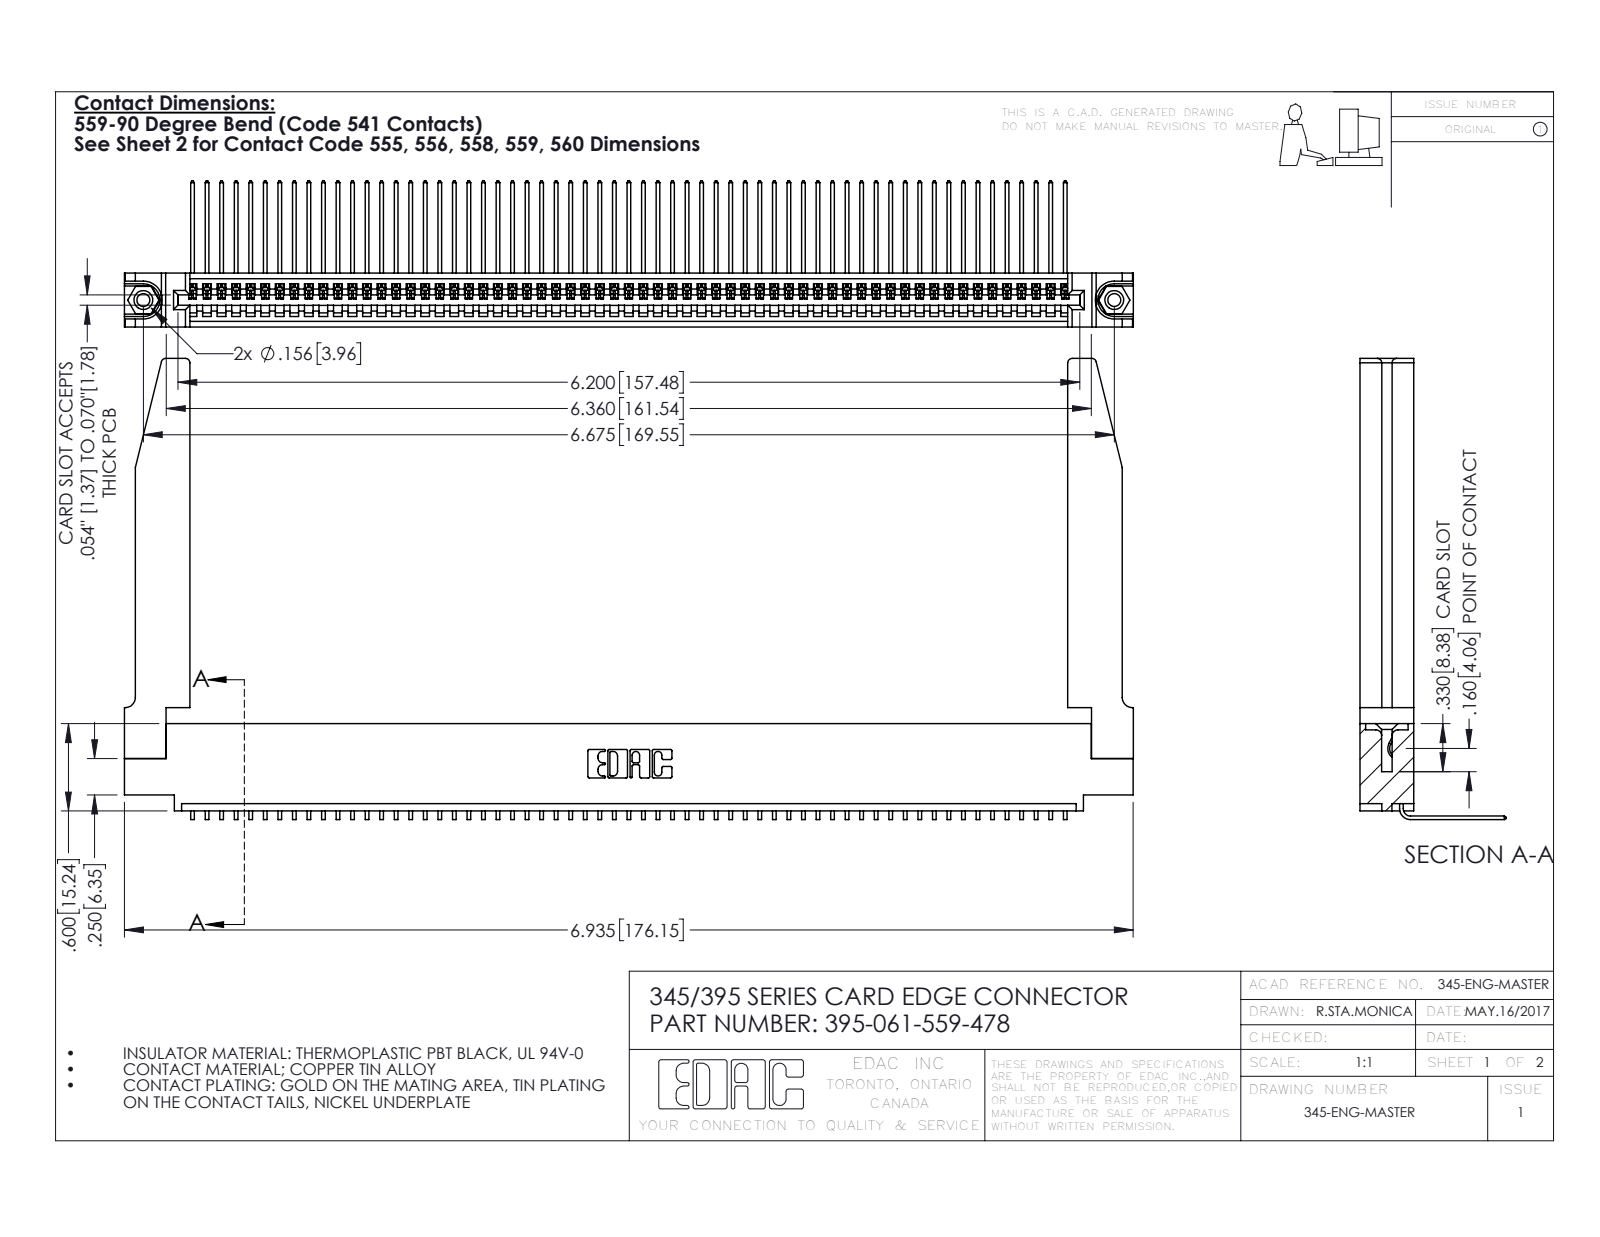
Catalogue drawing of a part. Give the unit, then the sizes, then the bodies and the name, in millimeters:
Units: millimetres
Overall size (bounding box): 176.2 × 80.5 × 25.5
Round holes (diameter × count): ⌀2.3 ×2, ⌀3.2 ×2, ⌀4 ×2, ⌀1.6 ×1
Round bosses / shafts (diameter × count): ⌀3.9 ×2
Partial cylindrical surfaces — rounded edges, fillets, slot ends (radius × count): R0.2 ×122, R0.3 ×22, R0.8 ×8, R0.2 ×6, R0.8 ×6, R0.7 ×3, R0.8 ×2, R1 ×2
Main face-to-face distances: 9.4, 1.8, 7.6, 2.5, 6.9, 0.6, 5.1, 5.7, 3.8, 3.8
Hole centre spacings: 6.9, 163.6, 169.5
Volume: 24 790 mm³ · Surface area: 30 990 mm²
Bodies: 66 solids, 4024 faces (2788 planar, 1184 cylindrical, 52 other)
Part name (STEP PRODUCT): 345 Part_0.110 Offset - 0.156 Dia-TH; 345-292-001_558 559 Tail - 1; 345-250-001_345-250-001-102; 395-061-559-478 (+1 more)
STEP written by: SolidWorks 2016 (CONFIG_CONTROL_DESIGN)
